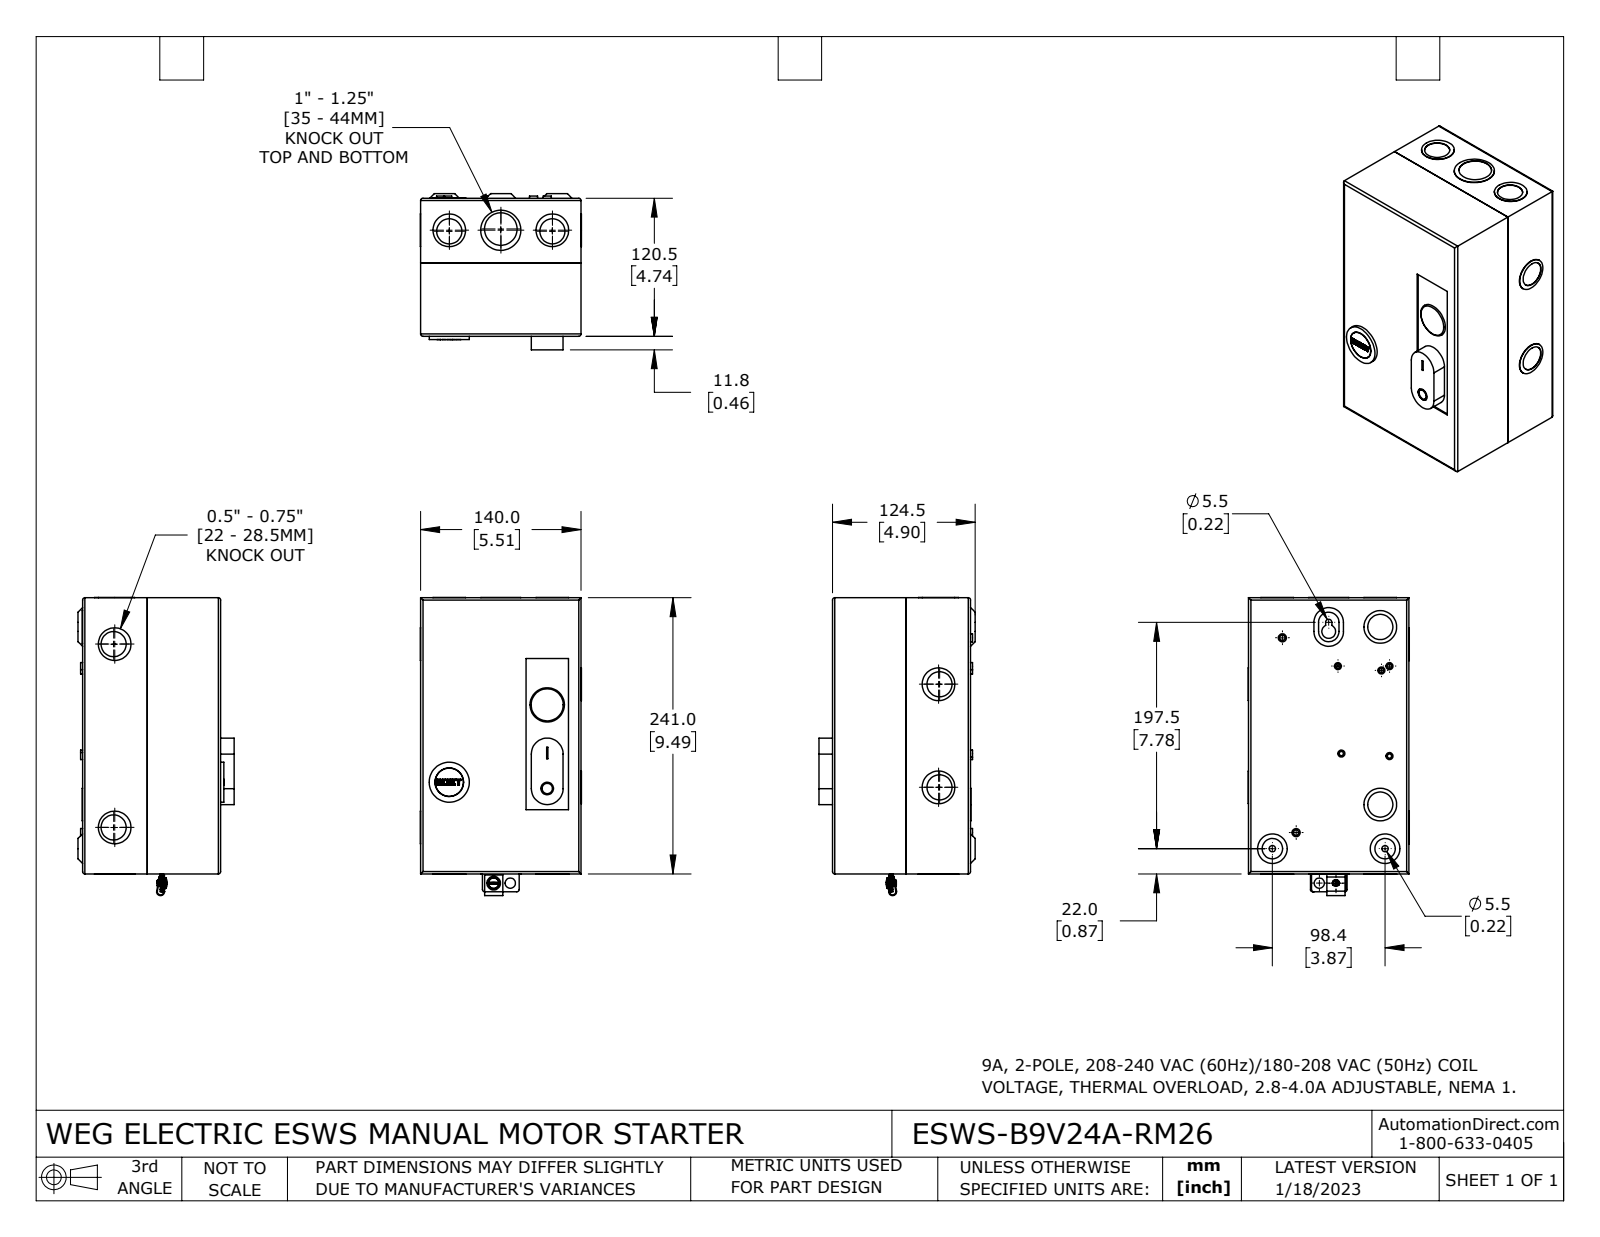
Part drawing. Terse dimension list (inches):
name: ESWS-B9V24A-RM26
written by: SolidWorks 2021 (CONFIG_CONTROL_DESIGN)
unit: in
bodies: 7 solids, 435 faces (168 planar, 230 cylindrical, 37 other)
size: 10.248 × 5.535 × 5.366
volume: 16.23 in³; area: 585.2 in²
holes: 5× ⌀0.146, 4× ⌀0.864, 2× ⌀0.183, 2× ⌀0.217, 2× ⌀0.354, 2× ⌀0.864, 2× ⌀0.866, 2× ⌀0.886, 1× ⌀0.256, 1× ⌀0.303, 1× ⌀0.433, 1× ⌀0.469
bosses: 6× ⌀1.124, 5× ⌀0.24, 2× ⌀1.122, 2× ⌀0.278, 1× ⌀1.38, 1× ⌀1.378, 1× ⌀1.193, 1× ⌀1.148
rounds: 34× R0.004, 13× R0.079, 4× R0.031, 3× R0.108, 2× R0.059, 2× R0.075, 2× R0.122, 2× R0.138
face distances: 0.047, 4.697, 5.465, 4.65, 9.441, 4.744, 5.417, 5.512, 0.071, 0.063
hole spacings: 0.571, 1.378, 1.773, 3.387, 3.543, 4.921, 5.995, 7.484
